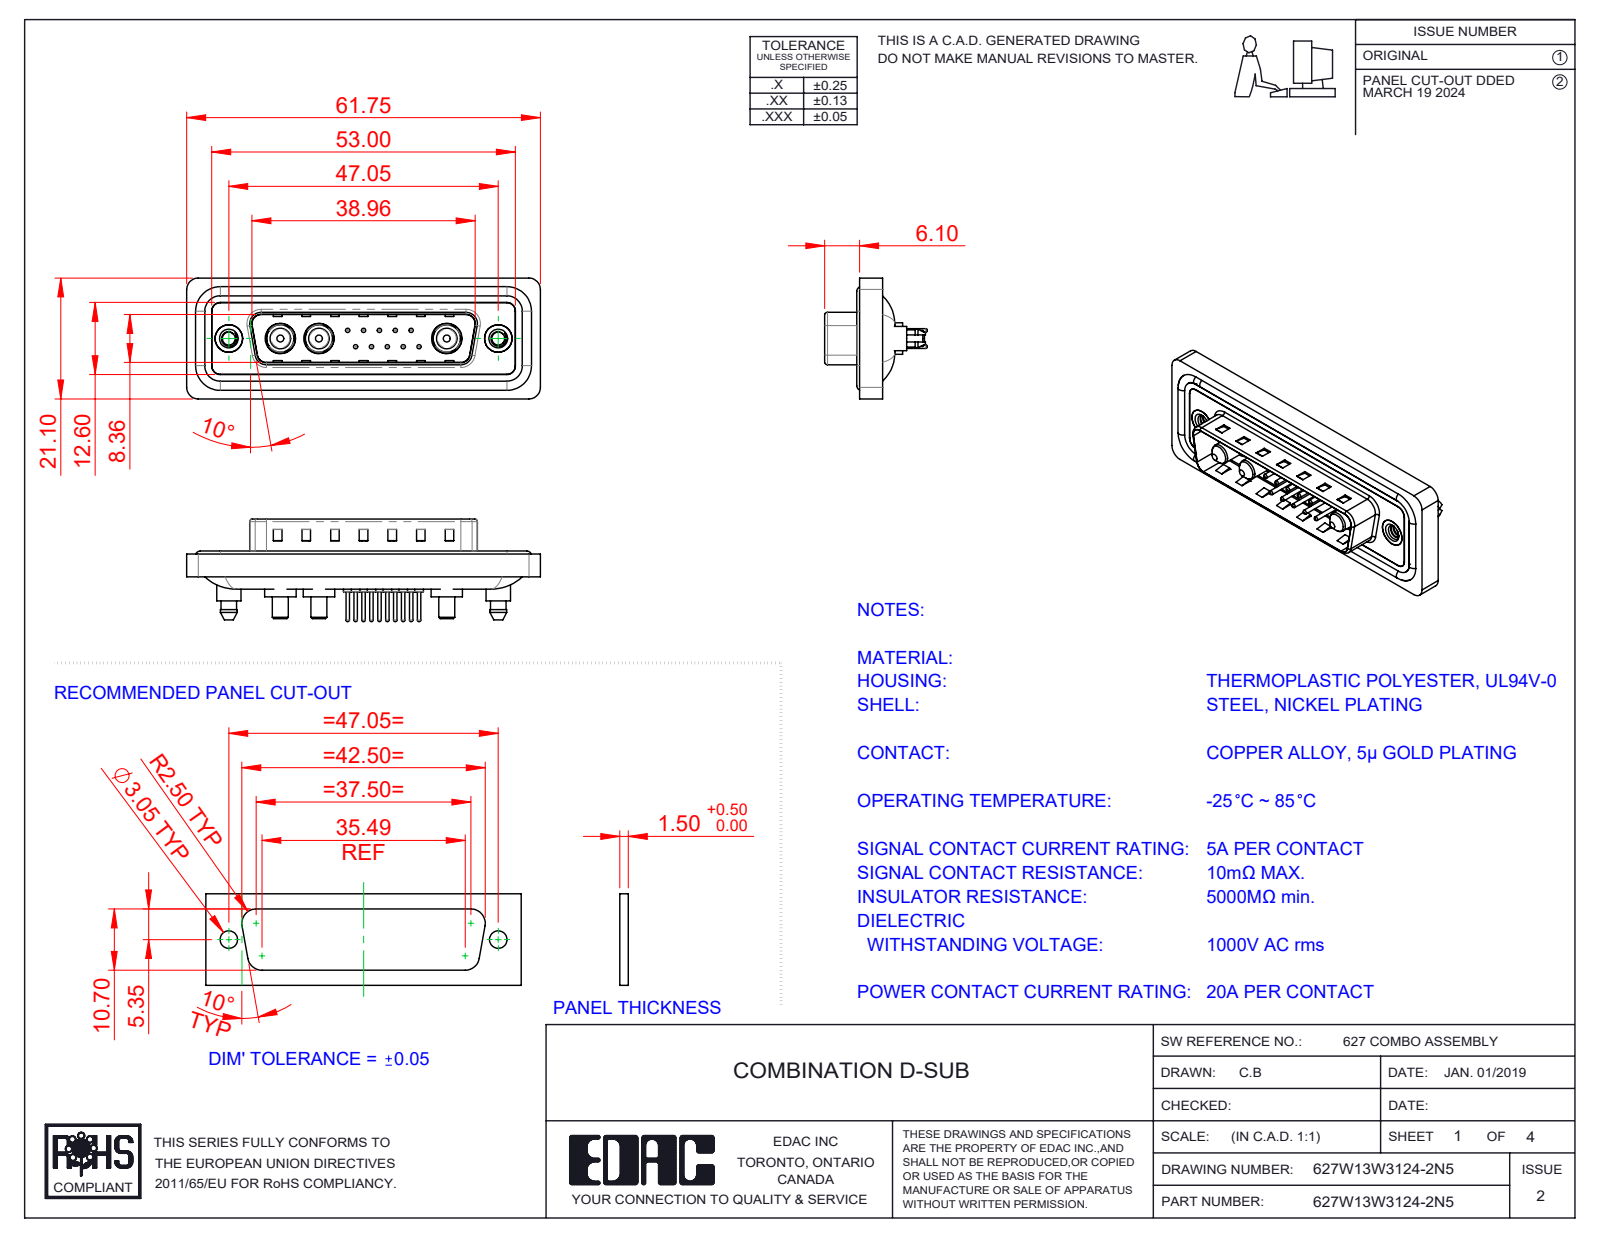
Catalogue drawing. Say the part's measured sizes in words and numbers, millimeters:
The part is named "627Combo Shell Front_25 Contacts; 627W13W3124-2N5; 627Combo Waterproof Housing_25 Contacts; 627Combo Contact Row 2_24 (+5 more)". Its 3-D file was written by "SolidWorks 2023 (CONFIG_CONTROL_DESIGN)". It is 23 solids with 1020 faces: 325 planar, 417 cylindrical and 278 other. Overall it measures 61.75 by 21.1 by 17.9 millimeters. Its volume is 7 469 cubic millimeters and its surface area 12 208 square millimeters. Round holes: 10 of diameter 0.75, 10 of diameter 1.6, 10 of diameter 2, 3 of diameter 4.85, 3 of diameter 5.3, 2 of diameter 2.26, 2 of diameter 4, 2 of diameter 4.8, 2 of diameter 5. Round bosses or shafts: 10 of diameter 1.5, 10 of diameter 0.6, 4 of diameter 1.6, 3 of diameter 5.5, 3 of diameter 5.2, 3 of diameter 4.75, 3 of diameter 3.75, 3 of diameter 3.6. Partial cylindrical surfaces (rounded edges, fillets, slot ends): 24 of radius 1.5, 18 of radius 2, 10 of radius 1.6, 8 of radius 0.5, 4 of radius 0.25, 4 of radius 0.6, 4 of radius 0.65, 4 of radius 0.9. The main face-to-face distances are 0.4, 1.5, 1.1, 1.6, 0.5, 3.1, 2.9, 0.82, 9.58, 4.1. The hole center spacings are 3.16, 2.77, 5.04, 5.54, 7.49, 5.03, 8.31, 10.11.
